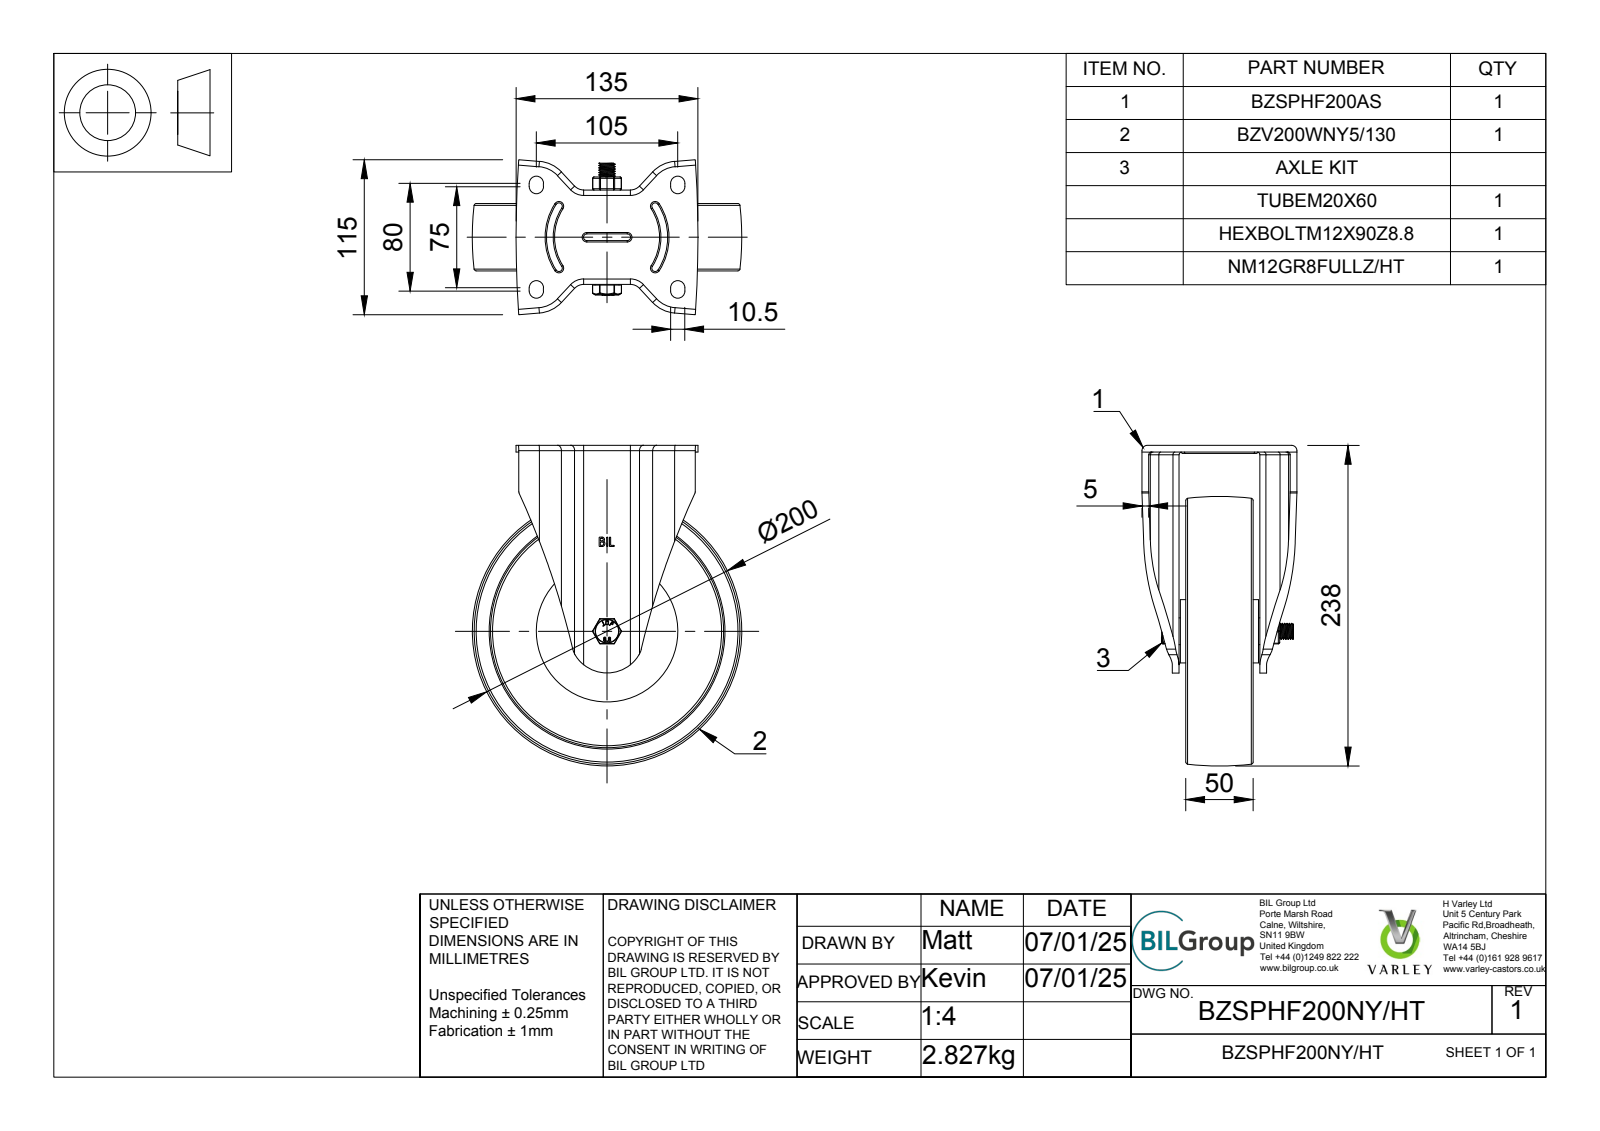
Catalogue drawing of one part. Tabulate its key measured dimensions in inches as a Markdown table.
| quantity | value |
| --- | --- |
| part name | BZSPHF200NY/HT v4; BZSPHF200AS - 60 v1; PRESSED STEEL BRACKET; BZV200WNY5130 v1 (+7 more) |
| STEP written by | Autodesk Translation Framework v13.20.0.188 (AP242_MANAGED_MODEL_BASED_3D_ENGINEERING_MIM_LF) |
| units | inches |
| bodies | 5 solids, 399 faces (135 planar, 154 cylindrical, 110 other) |
| overall size | 9.37 × 7.874 × 4.528 |
| volume | 62.49 in³ |
| surface area | 352.6 in² |
| round holes (diameter × count) | 0.472 × 1, 0.48 × 1, 0.492 × 1, 0.807 × 1, 6.811 × 1 |
| round bosses / shafts (diameter × count) | 1.85 × 1, 0.783 × 1, 0.699 × 1, 0.466 × 1, 0.387 × 1 |
| partial cylindrical surfaces (radius × count) | 0.039 × 22, 0.079 × 12, 0.157 × 10, 0.207 × 8, 0.02 × 6, 0.019 × 4, 0.035 × 4, 0.363 × 4 |
| main face-to-face distances | 0.197, 2.362, 0.551, 1.102, 1.654, 0.709, 0.394, 1.26, 2.559, 0.906 |
